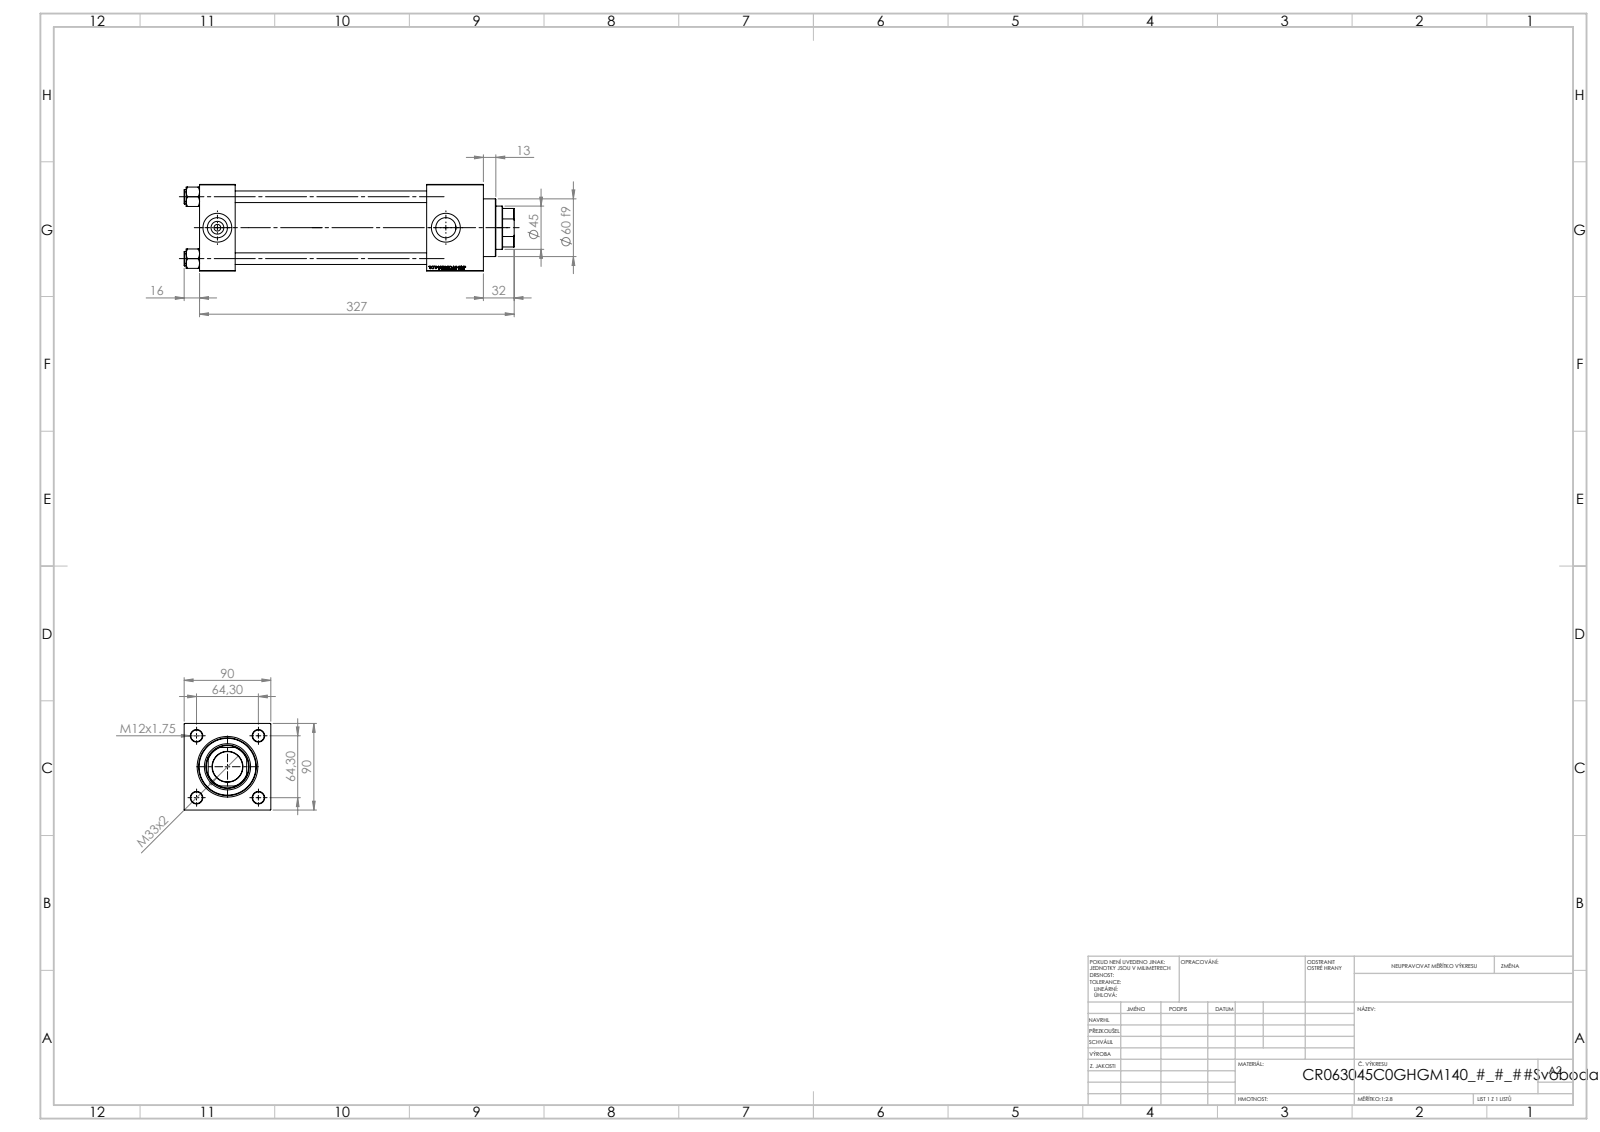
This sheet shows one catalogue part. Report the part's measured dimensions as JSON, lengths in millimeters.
{"part_name": "V215CR_C_TYCINKA; V215_VC_A; V215CR_C_Body; NUT_M5_C (+1 more)", "step_written_by": "SolidWorks 2019 (CONFIG_CONTROL_DESIGN)", "units": "millimeters", "bodies": {"solids": 11, "faces": 1145, "planar": 525, "cylindrical": 84, "other": 536}, "overall_size": [343, 90, 90], "volume_mm3": 1371000, "surface_area_mm2": 288890, "round_holes": [[12, 4], [7, 2], [20.96, 2], [30, 2], [31.5, 1], [45, 1], [48, 1], [50, 1], [60, 1], [63, 1]], "round_bosses_or_shafts": [[15, 4], [69, 1]], "partial_cylinders_radius": [[22, 1]], "face_to_face_distances": [90, 37, 59, 236, 199, 295, 258, 266.3, 229.3, 30.3], "hole_center_spacings": [45.47, 64.3, 90.93, 237.5]}
